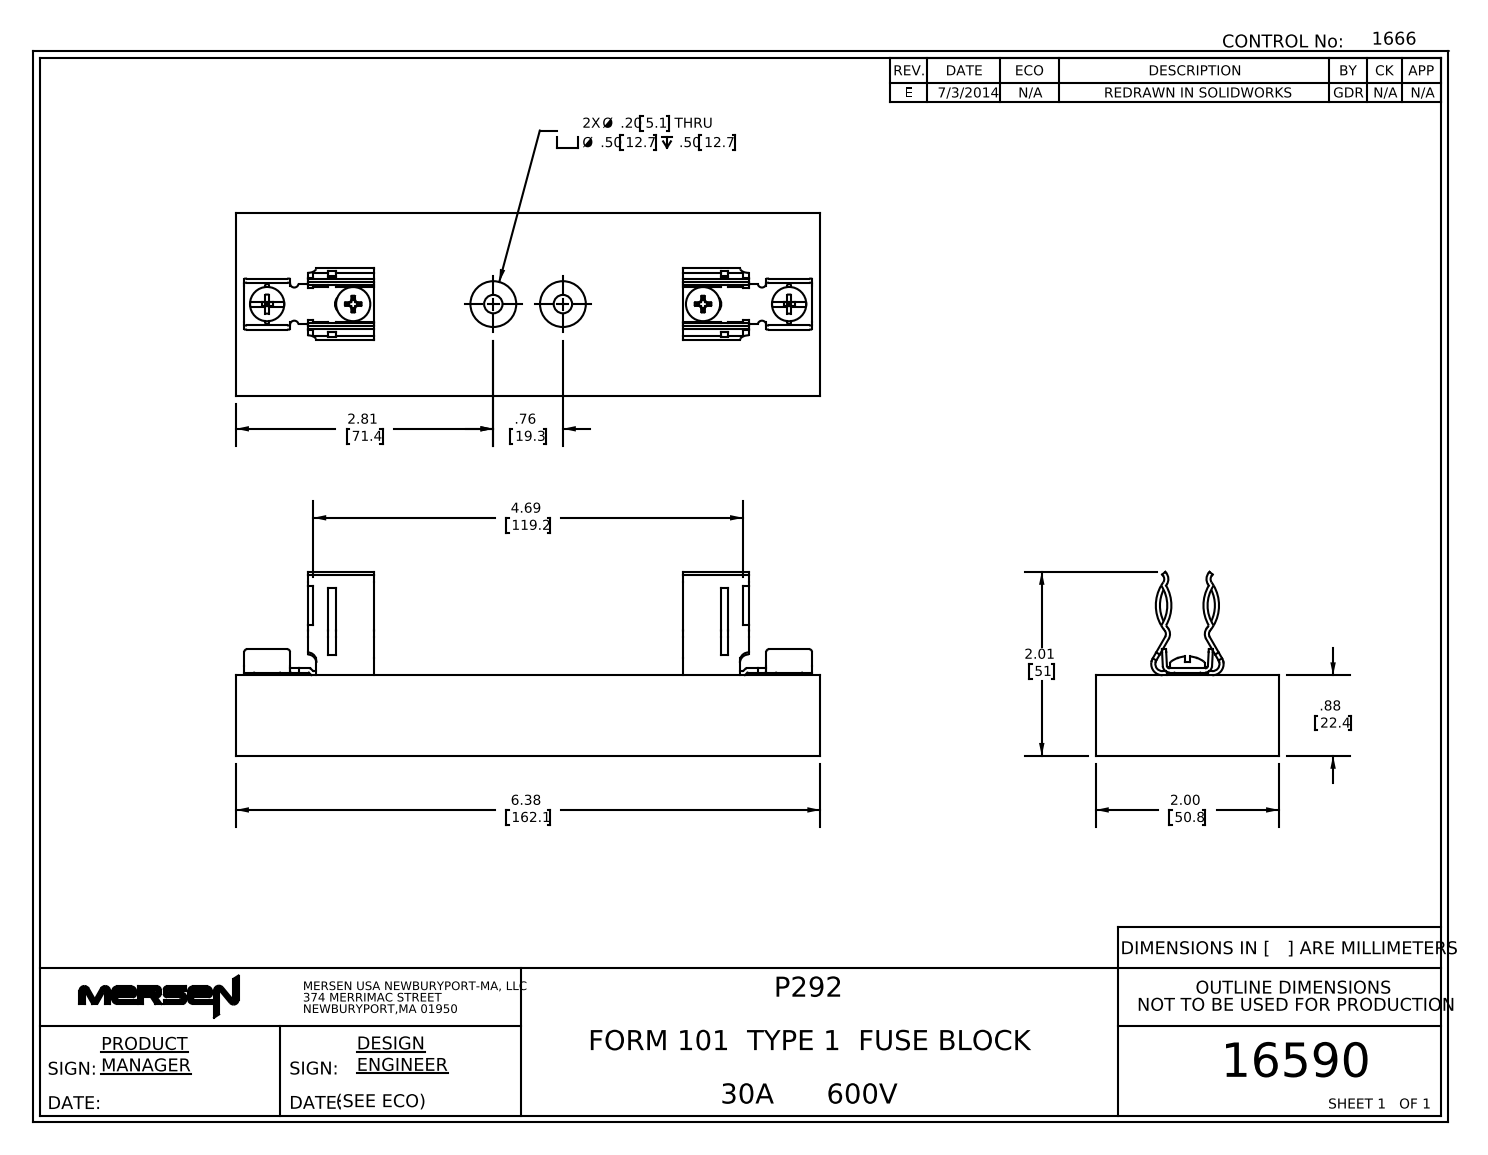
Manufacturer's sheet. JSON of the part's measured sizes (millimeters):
{"part_name": "16590revE", "step_written_by": "SolidWorks 2013 (AUTOMOTIVE_DESIGN)", "units": "millimeters", "bodies": {"solids": 0, "faces": 339, "planar": 173, "cylindrical": 132, "other": 34}, "overall_size": [162.1, 51, 50.8], "round_bosses_or_shafts": [[12.7, 2], [9.5, 2], [9.5, 2], [5.1, 2]], "partial_cylinders_radius": [[0.1, 8], [0.5, 4], [0.8, 4], [1.2, 4], [1.6, 4], [2.7, 4], [9.9, 4], [11, 4]], "face_to_face_distances": [22.4, 50.8, 162.1, 1.1, 1.1, 23.5, 24.3, 1.9, 0.8, 38.2]}
